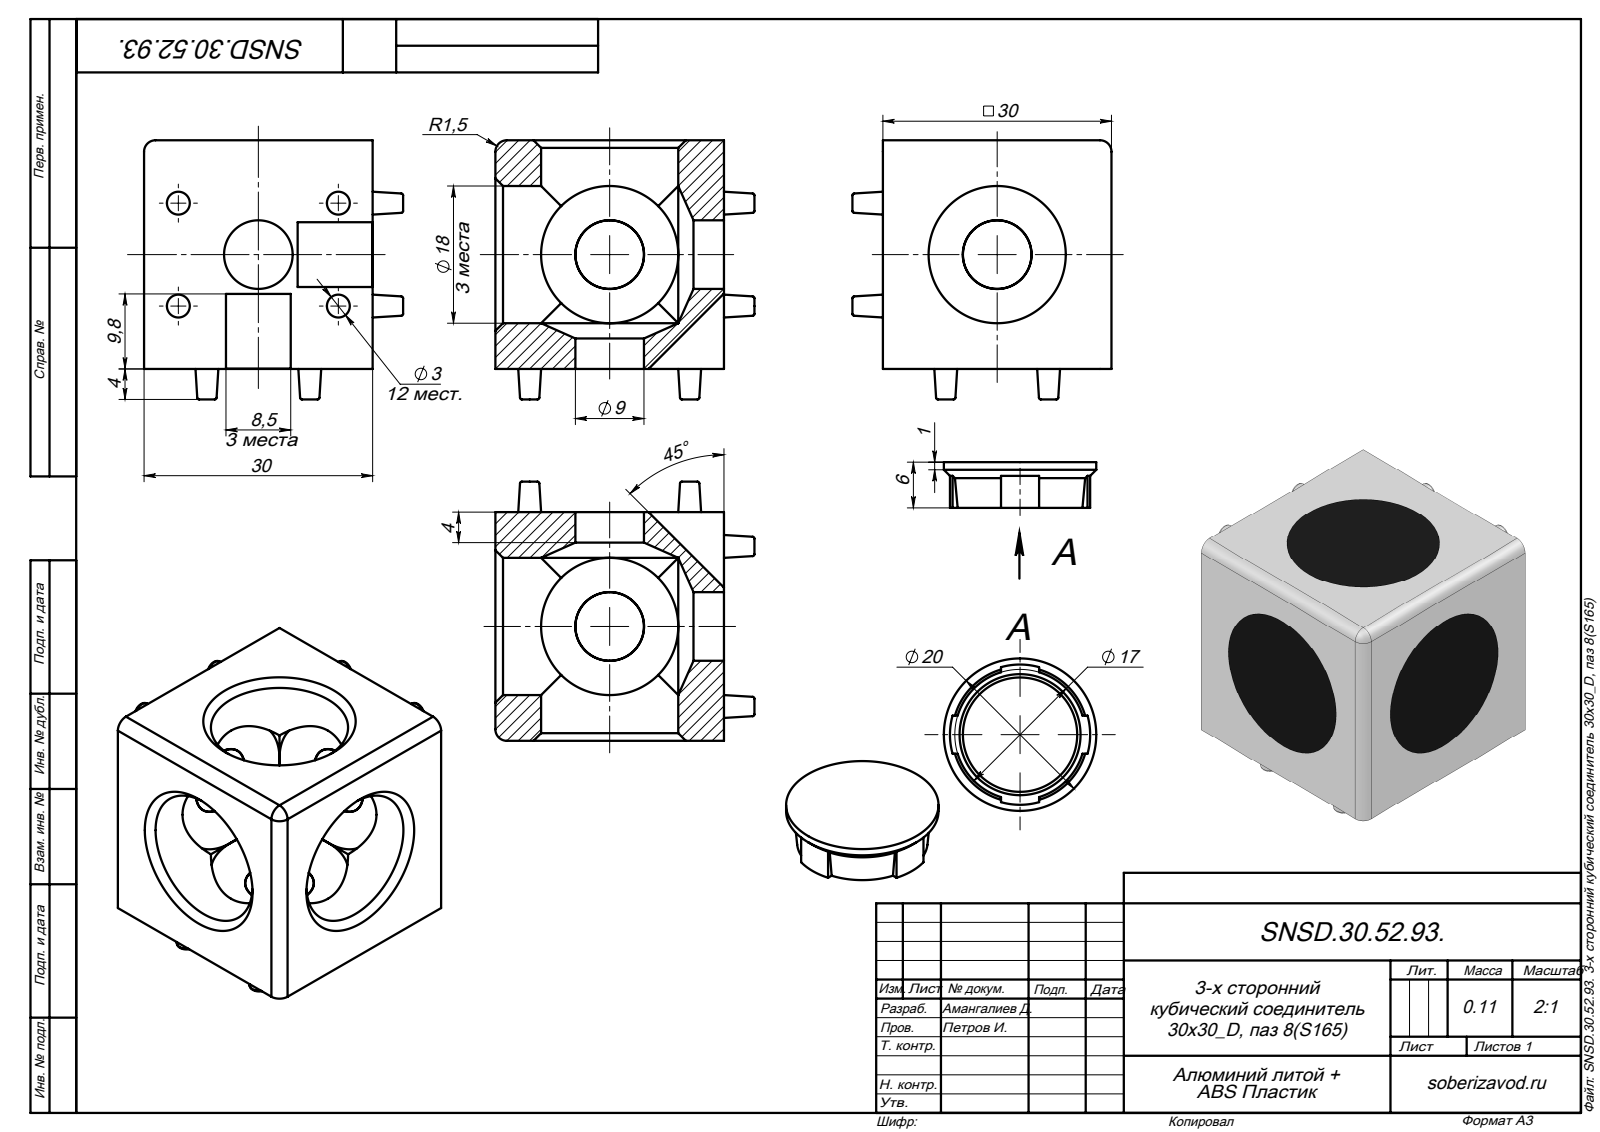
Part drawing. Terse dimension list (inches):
name: SNSD.30.51.58. 3-х сторонний соединитель 45х45, паз 10(E51)S165; SNSD.30.51.58. 3-х сторонний соединитель 45х45, паз 10(E51)S165_00
written by: SolidWorks 2014 (AUTOMOTIVE_DESIGN)
unit: in
bodies: 4 solids, 202 faces (69 planar, 48 cylindrical, 85 other)
size: 1.339 × 1.339 × 1.339
volume: 0.986 in³; area: 16.42 in²
holes: 3× ⌀0.354, 3× ⌀0.709
bosses: 3× ⌀0.787
rounds: 3× R0.059, 3× R0.362
face distances: 1.181, 1.142, 0.039, 0.423, 0.758, 0.197, 0.719, 0.384, 0.335, 0.945
